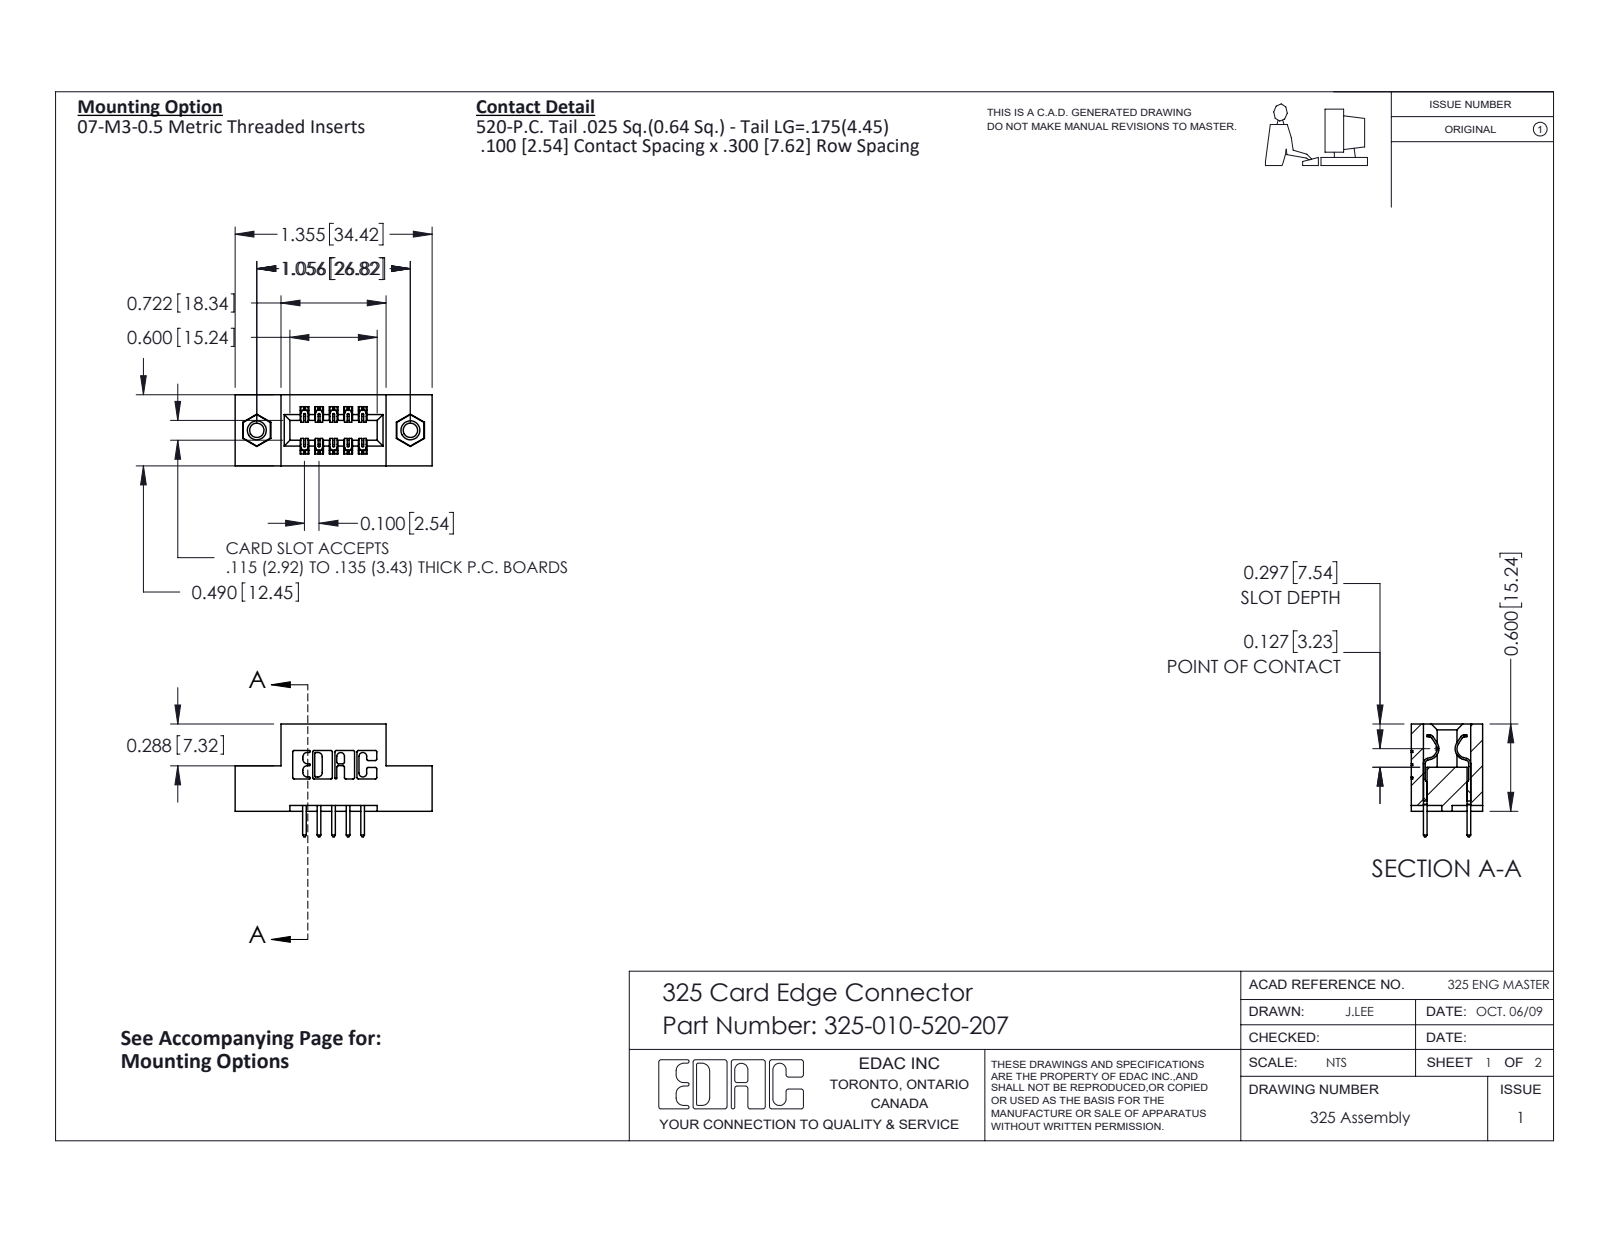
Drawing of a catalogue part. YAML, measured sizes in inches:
part_name: "345-250-001_345-250-005-103; 325 Part_TI; 325-010-520-207; 325-292-001_325-293-120"
step_written_by: "SolidWorks 2016 (CONFIG_CONTROL_DESIGN)"
units: inches
bodies: {solids: 13, faces: 694, planar: 462, cylindrical: 216, other: 16}
overall_size: [1.355, 0.775, 0.49]
volume: 0.25
surface_area: 6.334
round_holes:
  - {diameter: 0.098, count: 2}
  - {diameter: 0.125, count: 2}
  - {diameter: 0.16, count: 2}
round_bosses_or_shafts:
  - {diameter: 0.155, count: 2}
partial_cylinders:
  - {radius: 0.01, count: 22}
  - {radius: 0.006, count: 15}
  - {radius: 0.01, count: 10}
  - {radius: 0.007, count: 6}
  - {radius: 0.031, count: 6}
  - {radius: 0.026, count: 3}
  - {radius: 0.014, count: 2}
  - {radius: 0.022, count: 2}
face_to_face_distances: [0.3, 0.1, 0.49, 0.083, 0.407, 0.04, 0.2, 0.06, 0.312, 0.107]
hole_center_spacings: [1.056]
